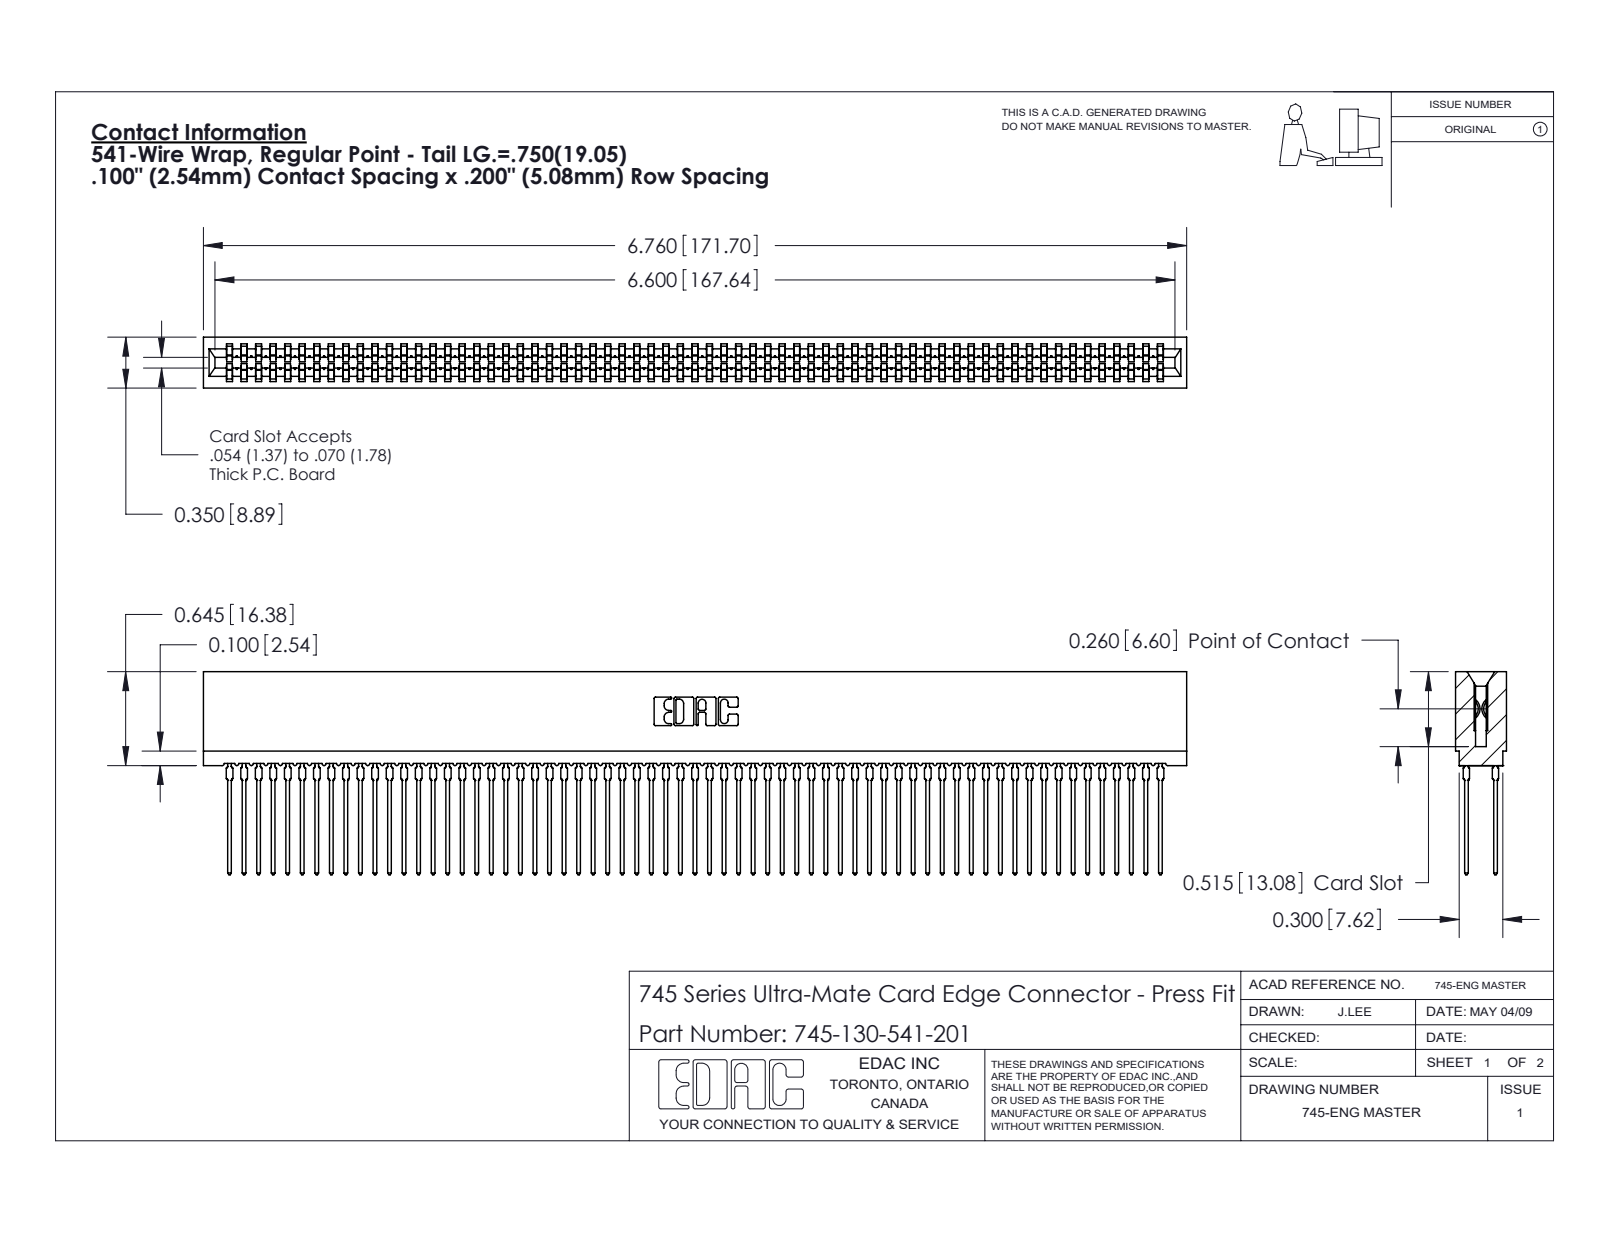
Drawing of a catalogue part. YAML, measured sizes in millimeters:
part_name: "745-130-541-201; 745-292-001_541; 745 Part_Insulator Option - 01"
step_written_by: "SolidWorks 2020 (CONFIG_CONTROL_DESIGN)"
units: millimeters
bodies: {solids: 131, faces: 11730, planar: 6035, cylindrical: 2315, other: 3380}
overall_size: [171.7, 35.5, 8.9]
volume: 16000
surface_area: 35560
partial_cylinders:
  - {radius: 0.5, count: 260}
  - {radius: 0.4, count: 130}
  - {radius: 0.3, count: 22}
  - {radius: 0.1, count: 8}
  - {radius: 0.3, count: 8}
  - {radius: 0.2, count: 6}
  - {radius: 0.8, count: 6}
  - {radius: 0.7, count: 3}
face_to_face_distances: [1.6, 7.3, 5.1, 8.9, 2.2, 6.7, 0.6, 1.1, 7.7, 0.5]
